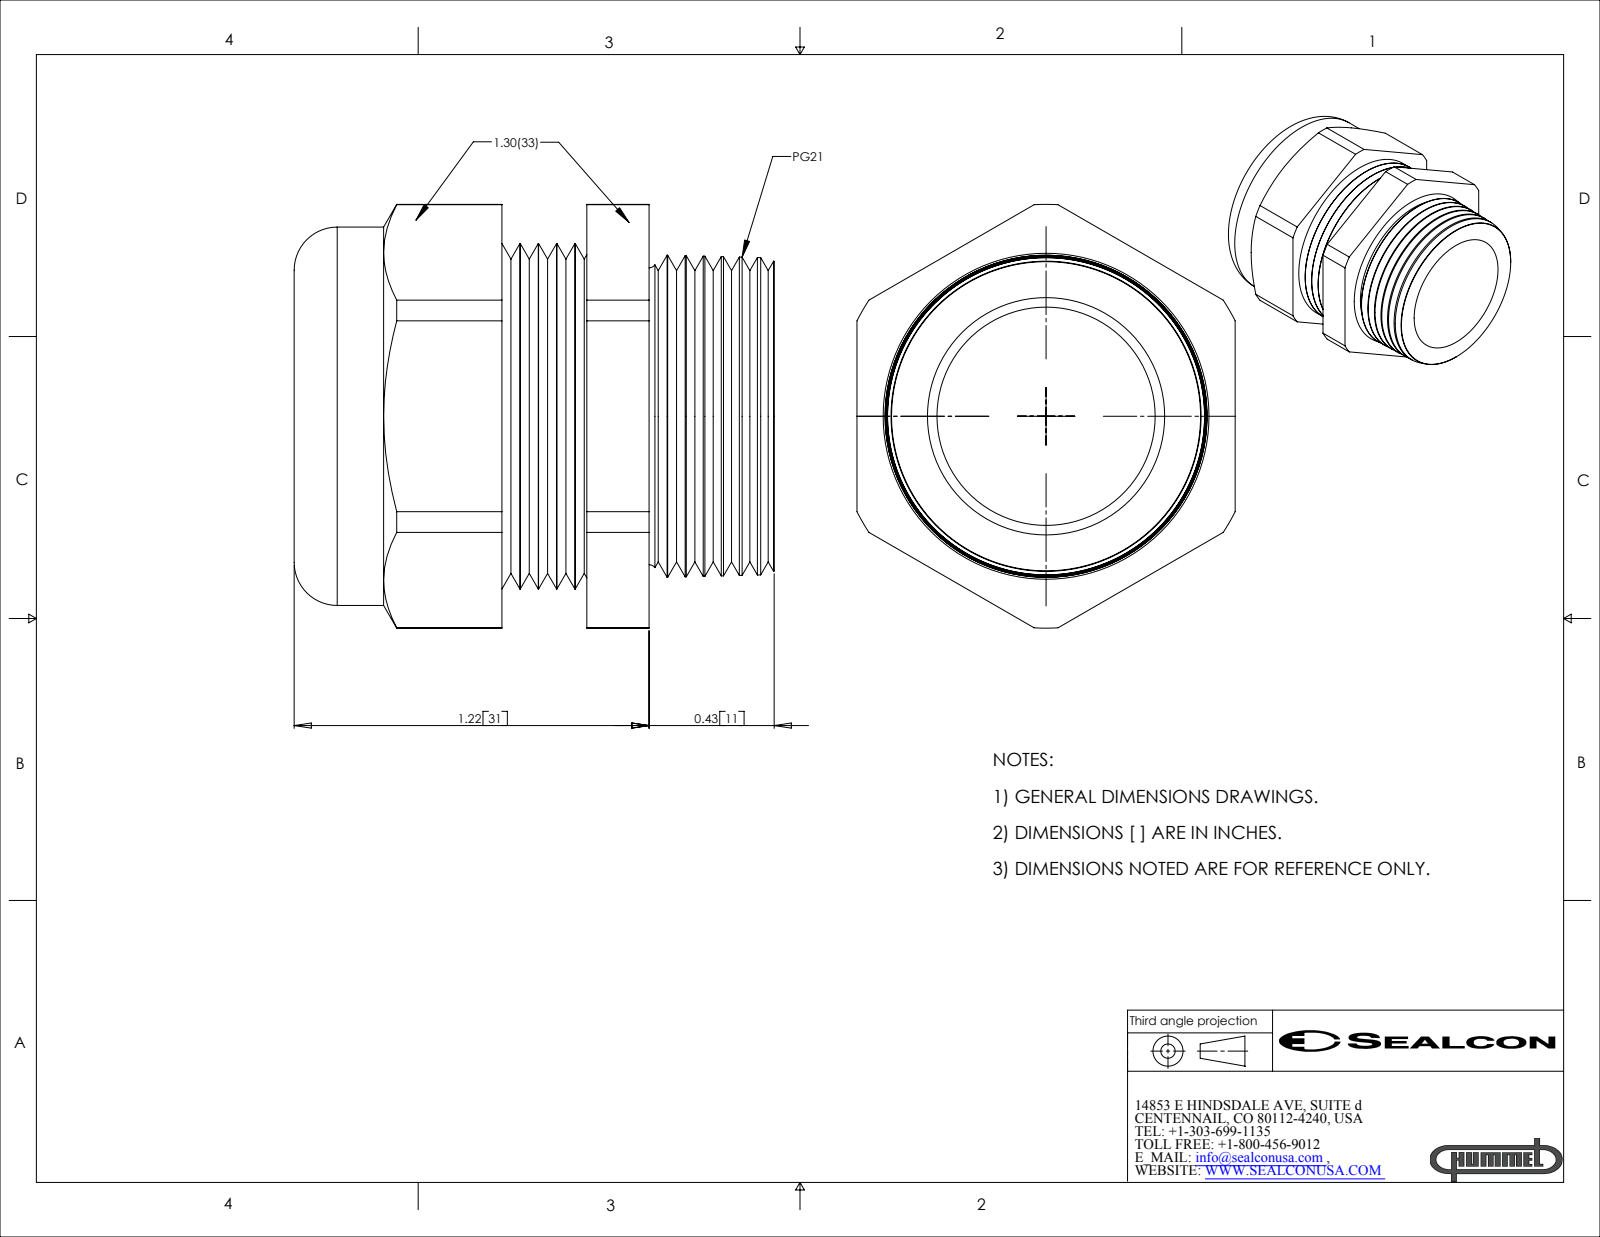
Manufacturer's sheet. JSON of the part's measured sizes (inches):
{"part_name": "CD21AA-GY", "step_written_by": "SolidWorks 2007 (CONFIG_CONTROL_DESIGN)", "units": "inches", "bodies": {"solids": 2, "faces": 130, "planar": 20, "cylindrical": 32, "other": 78}, "overall_size": [1.65, 1.456, 1.3], "volume_in3": 1.185, "surface_area_in2": 17.65, "round_holes": [[0.75, 1], [0.943, 1]], "round_bosses_or_shafts": [[1.3, 1], [1.187, 1]], "partial_cylinders_radius": [[0.728, 1]], "face_to_face_distances": [1.3, 0.913, 1.343, 0.43, 0.699, 0.214, 0.644, 0.407, 0.292, 0.506]}
